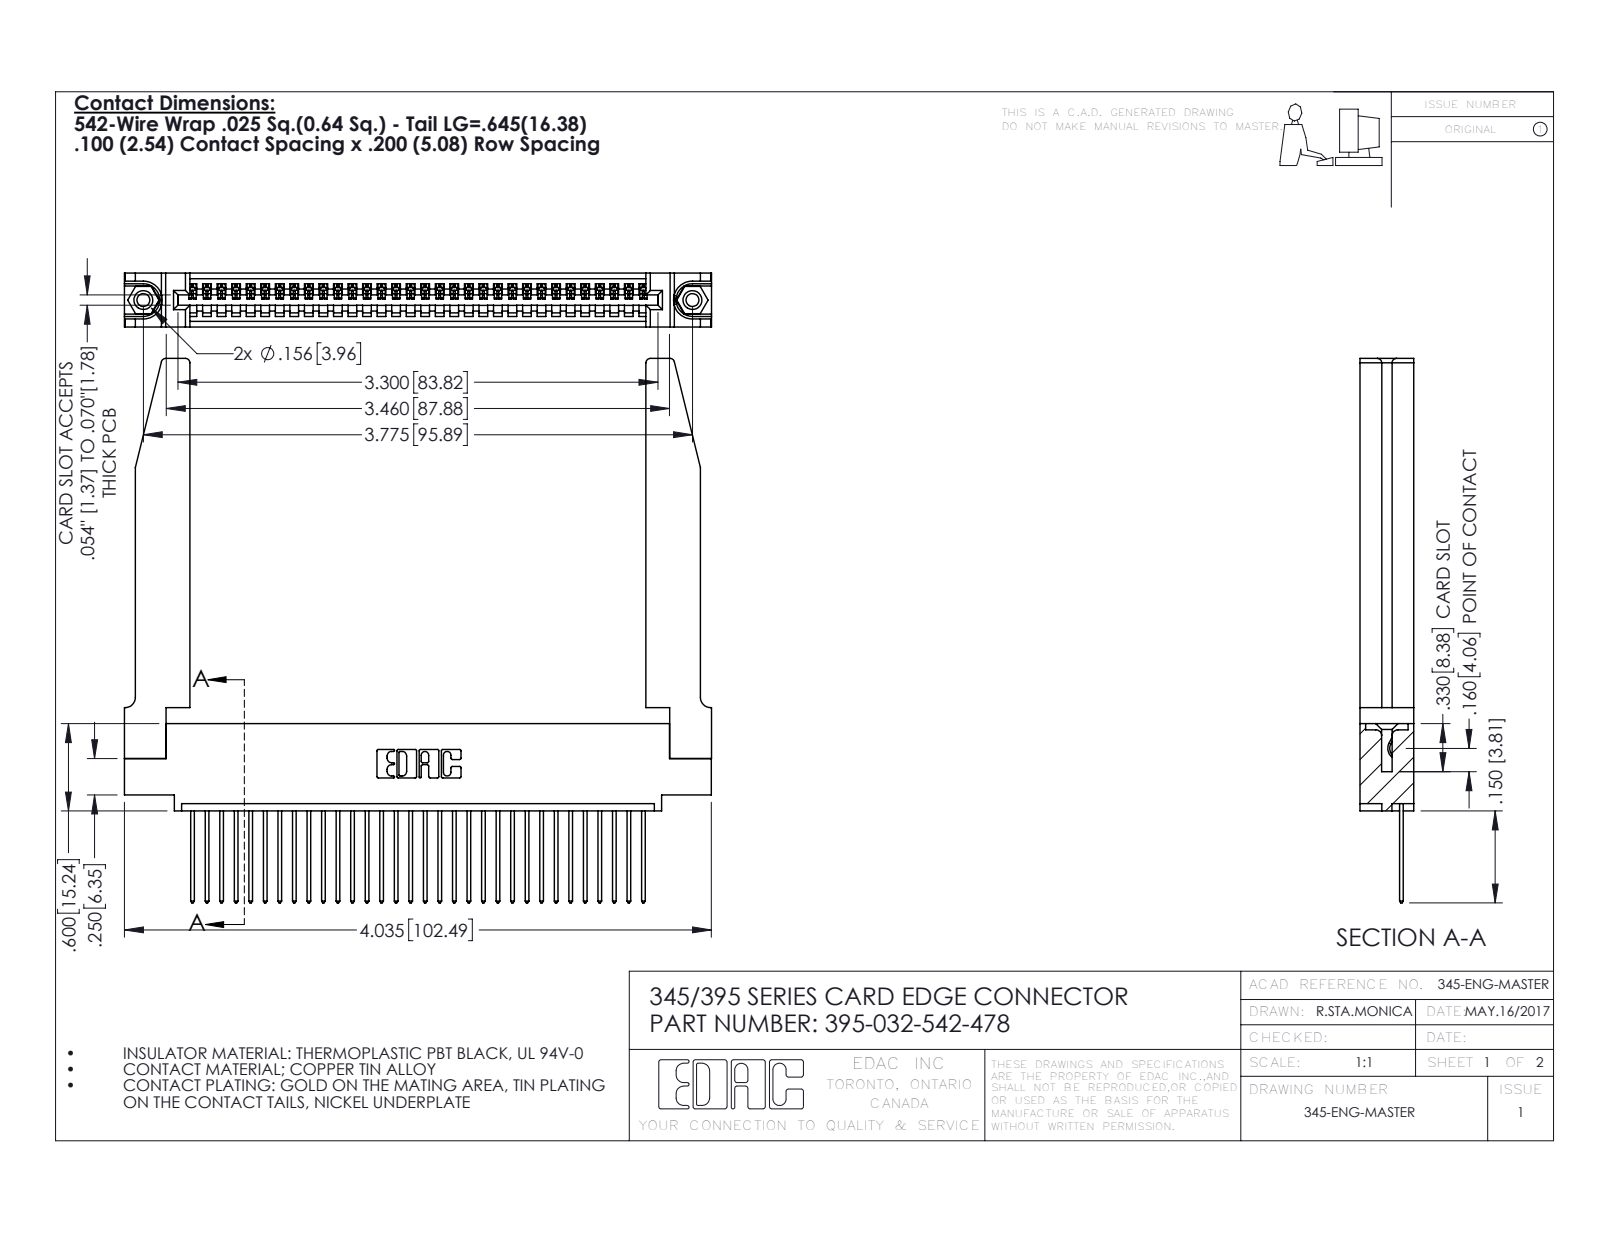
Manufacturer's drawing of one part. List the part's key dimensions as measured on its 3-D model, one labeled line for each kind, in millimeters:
Part name (STEP PRODUCT): 345-220-078_345-220-078; 345-292-001_345-293-142; 345 Part_0.110 Offset - 0.156 Dia-TH; 345-250-001_345-250-001-102 (+1 more)
STEP written by: SolidWorks 2016 (CONFIG_CONTROL_DESIGN)
Units: millimetres
Bodies: 37 solids, 2220 faces (1506 planar, 662 cylindrical, 52 other)
Overall size (bounding box): 102.5 × 95 × 9.4
Volume: 17 420 mm³ · Surface area: 20 070 mm²
Round holes (diameter × count): ⌀2.3 ×2, ⌀3.2 ×2, ⌀4 ×2, ⌀1.6 ×1
Round bosses / shafts (diameter × count): ⌀3.9 ×2
Partial cylindrical surfaces — rounded edges, fillets, slot ends (radius × count): R0.2 ×64, R0.3 ×64, R0.3 ×22, R0.8 ×8, R0.2 ×6, R0.8 ×6, R0.7 ×3, R0.8 ×2
Main face-to-face distances: 9.4, 1.8, 7.6, 2.5, 6.9, 0.6, 5.1, 3.8, 3.8, 5.7
Hole centre spacings: 6.9, 89.9, 95.9
